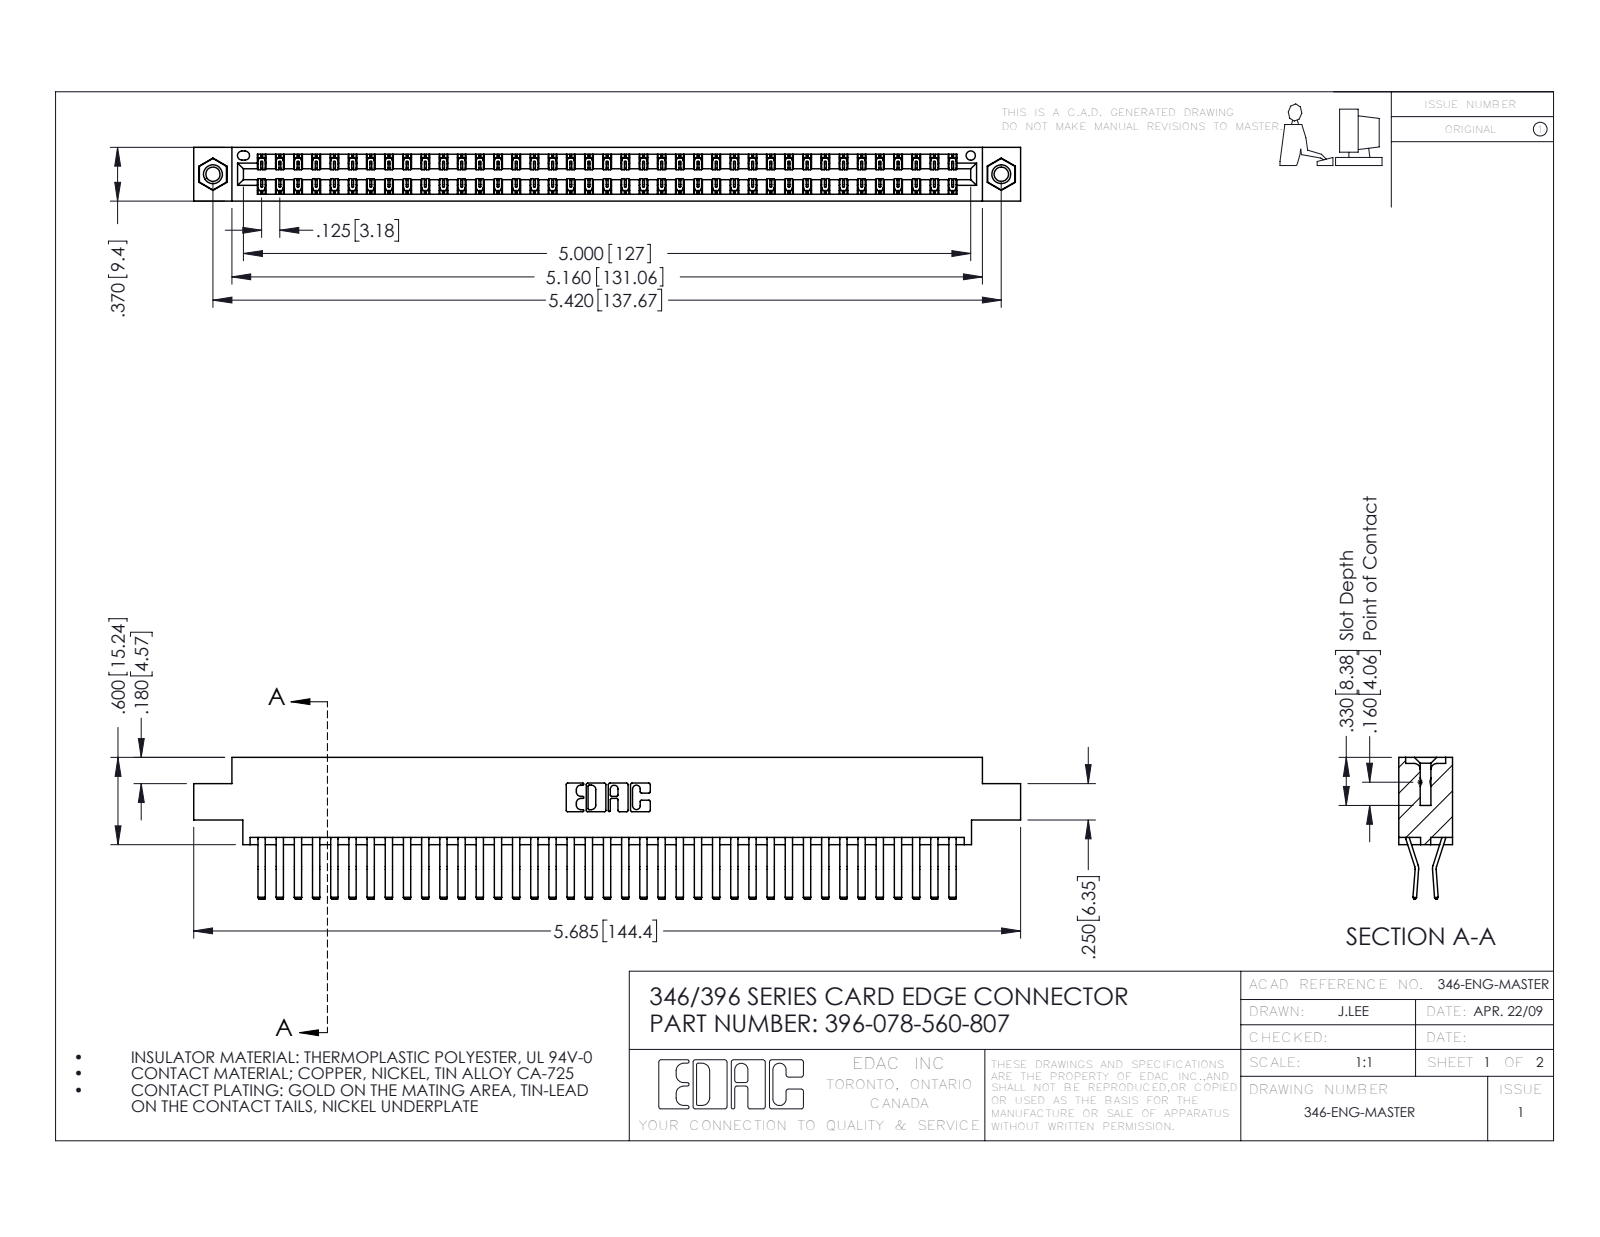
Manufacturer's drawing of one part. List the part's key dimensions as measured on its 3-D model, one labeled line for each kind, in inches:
Part name (STEP PRODUCT): 346 Part_0.170 Offset - 0.156 Dia-TI; 396-078-560-807; 345-292-001_560 Tail; 345-250-001_345-250-005-103
STEP written by: SolidWorks 2016 (CONFIG_CONTROL_DESIGN)
Units: inches
Bodies: 81 solids, 4398 faces (2842 planar, 1540 cylindrical, 16 other)
Overall size (bounding box): 5.685 × 0.975 × 0.37
Volume: 0.879 in³ · Surface area: 33.05 in²
Round holes (diameter × count): ⌀0.098 ×2, ⌀0.125 ×2, ⌀0.156 ×2, ⌀0.064 ×1
Round bosses / shafts (diameter × count): ⌀0.155 ×2
Partial cylindrical surfaces — rounded edges, fillets, slot ends (radius × count): R0.006 ×117, R0.01 ×22, R0.007 ×6, R0.031 ×6, R0.026 ×3, R0.01 ×2, R0.014 ×2, R0.022 ×2
Main face-to-face distances: 0.048, 0.322, 0.37, 0.025, 0.25, 0.072, 0.298, 0.275, 0.222, 0.148
Hole centre spacings: 0.246, 5.211, 5.42
